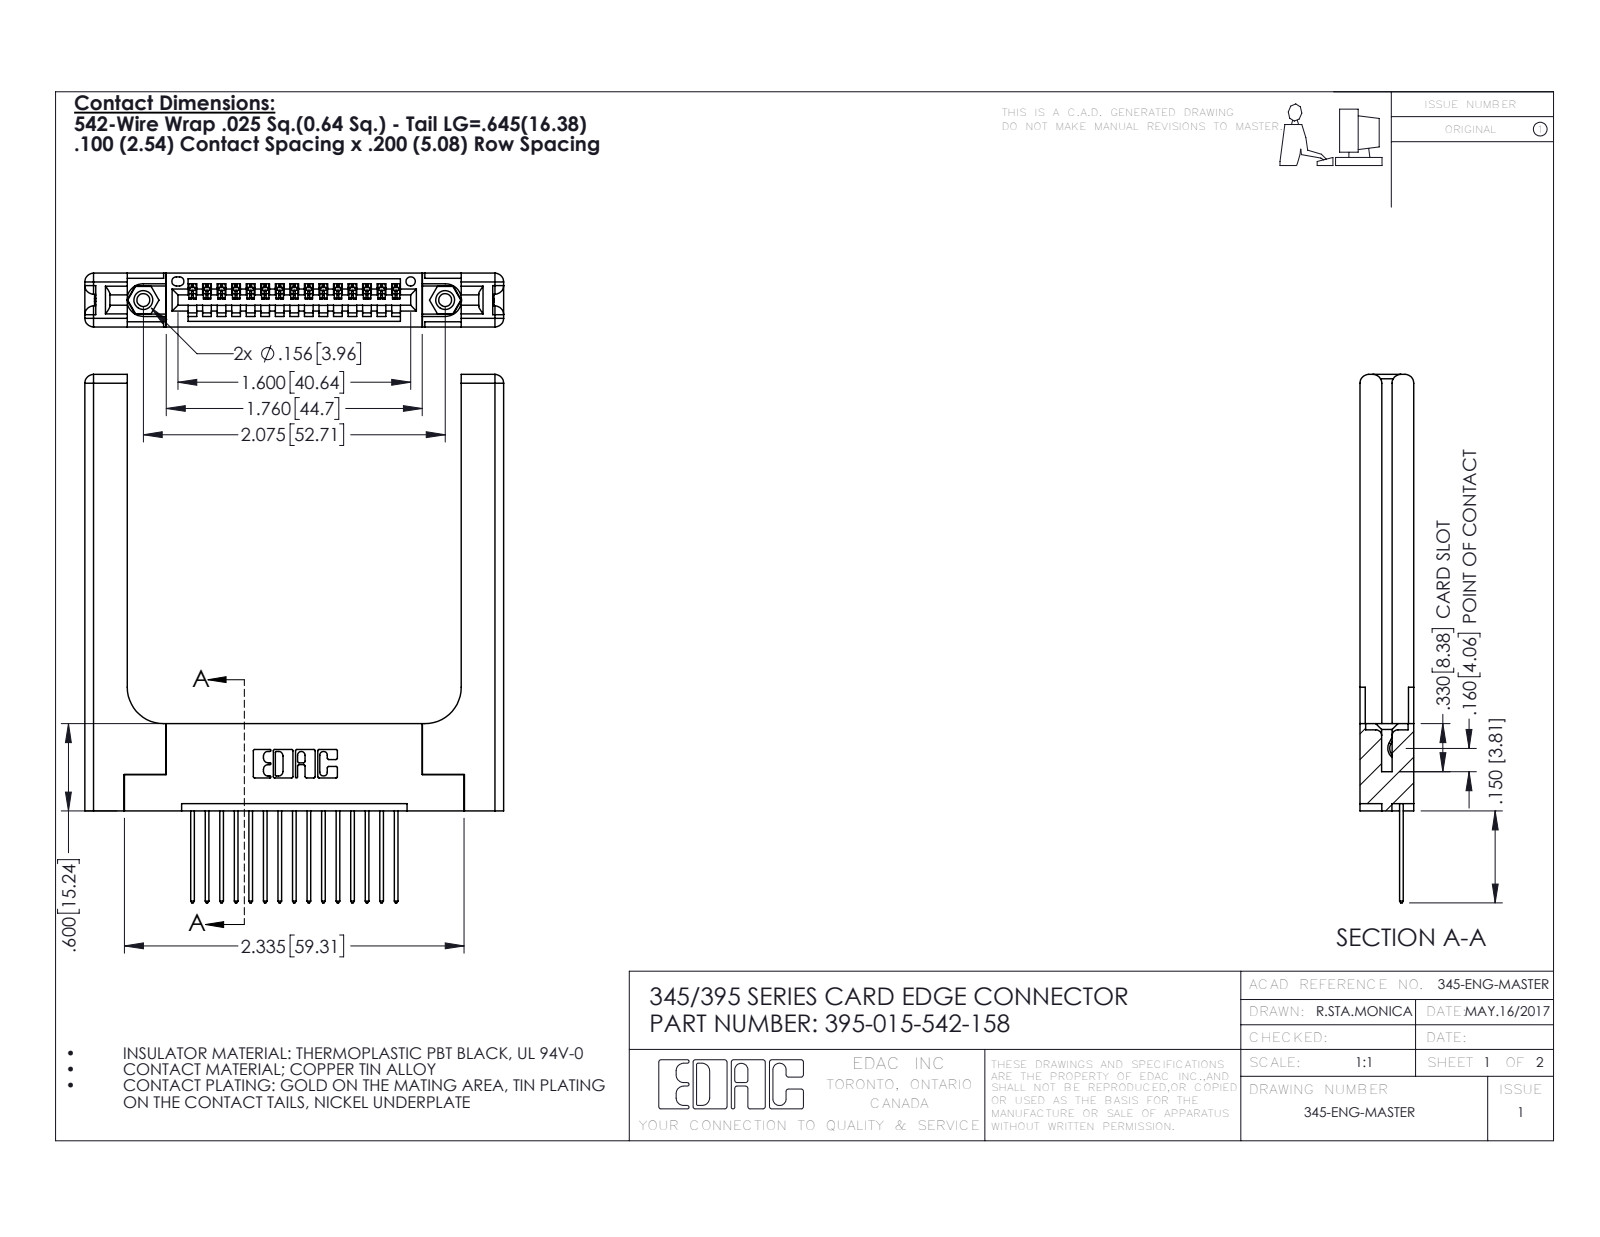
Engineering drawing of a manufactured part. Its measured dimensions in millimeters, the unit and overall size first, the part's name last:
Units: millimetres
Overall size (bounding box): 92.3 × 73.1 × 9.4
Round holes (diameter × count): ⌀2.3 ×2, ⌀3.2 ×2, ⌀4 ×2, ⌀1.6 ×1
Round bosses / shafts (diameter × count): ⌀3.9 ×2
Partial cylindrical surfaces — rounded edges, fillets, slot ends (radius × count): R0.2 ×30, R0.3 ×30, R0.3 ×22, R1.5 ×16, R0.2 ×6, R0.8 ×6, R0.7 ×3, R0.8 ×2
Main face-to-face distances: 9.4, 1.8, 7.6, 3.8, 2, 3.8, 5.1, 5.6, 2.5, 6.9
Hole centre spacings: 6.9, 46.8, 52.7
Volume: 15 300 mm³ · Surface area: 14 130 mm²
Bodies: 20 solids, 1252 faces (828 planar, 364 cylindrical, 60 other)
Part name (STEP PRODUCT): 395-015-542-158; 345-250-001_345-250-001-102; 345-220-058_345-220-058; 345-292-001_345-293-142 (+1 more)
STEP written by: SolidWorks 2016 (CONFIG_CONTROL_DESIGN)
